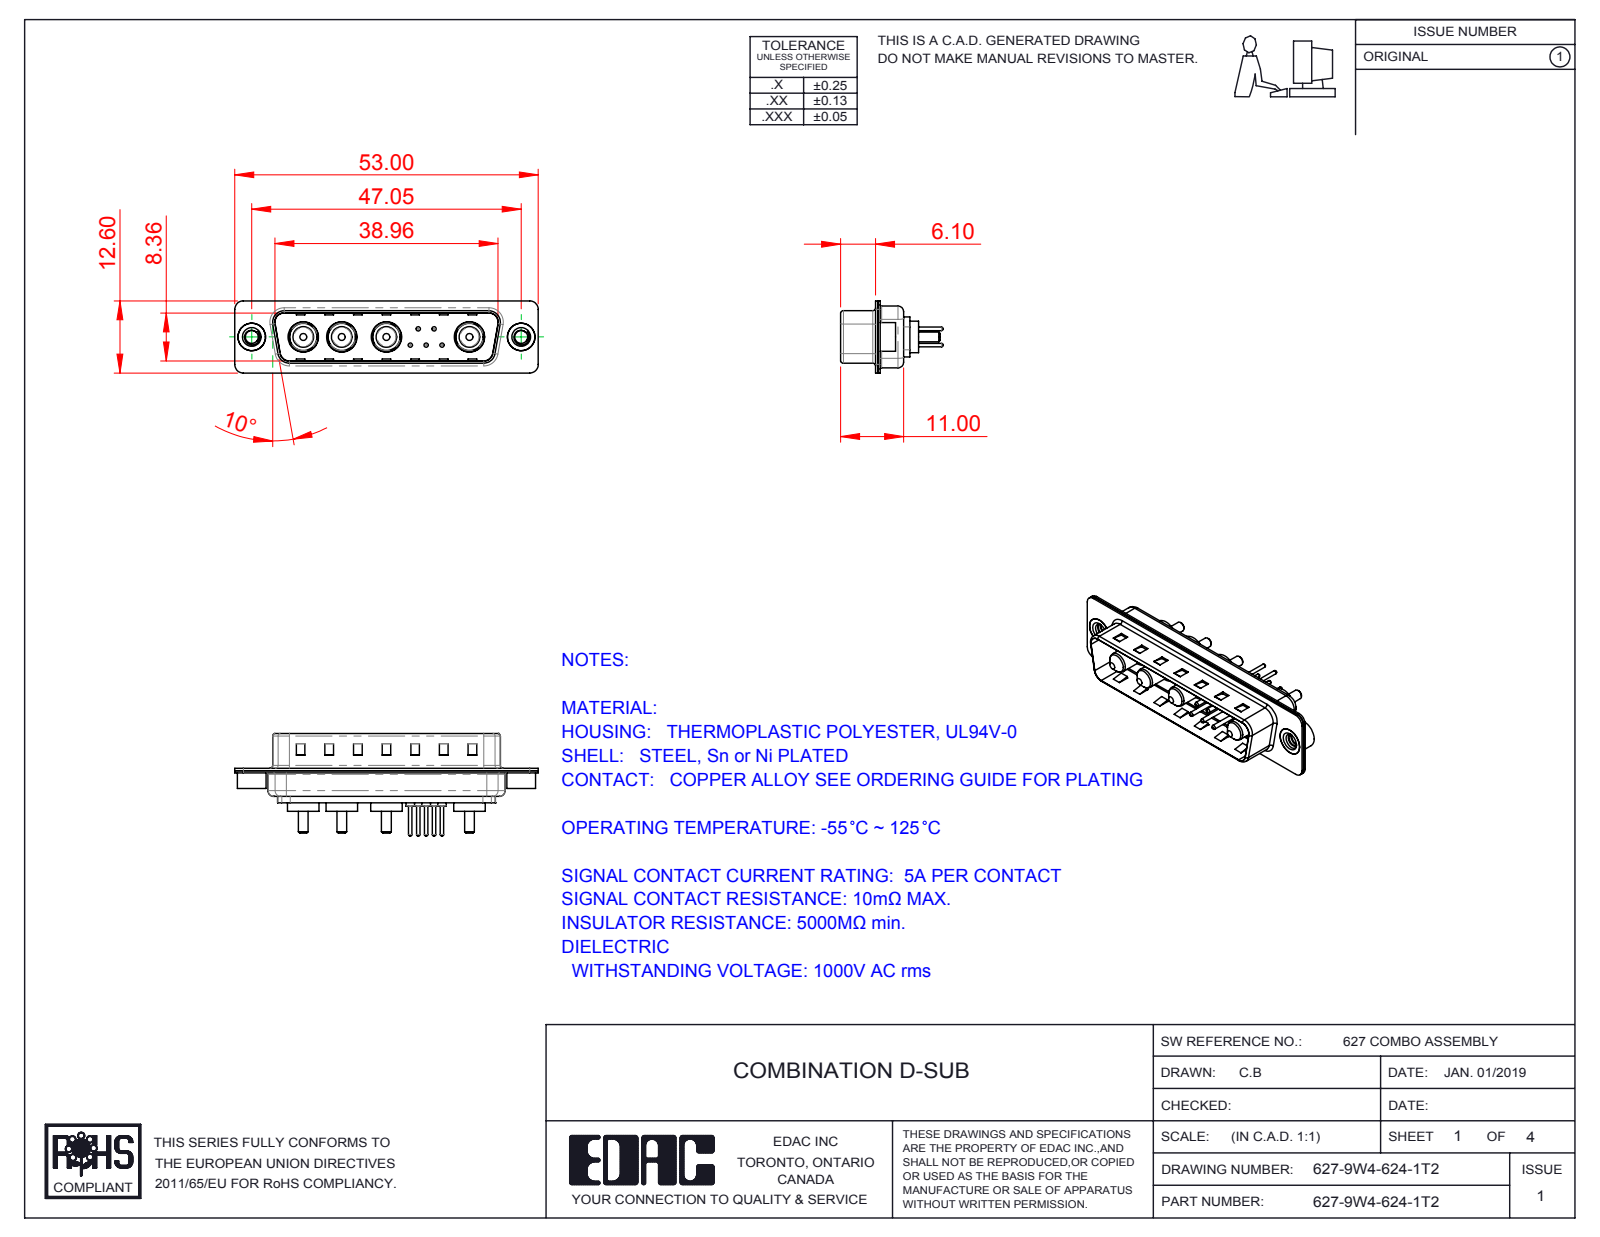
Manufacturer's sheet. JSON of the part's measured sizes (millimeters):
{"part_name": "627Combo Shell Rear_25 Contacts; 627Combo Housing_9W4; 627Combo Contact Row 1_24; 627Combo Contact Row 2_24 (+4 more)", "step_written_by": "SolidWorks 2016 (CONFIG_CONTROL_DESIGN)", "units": "millimeters", "bodies": {"solids": 18, "faces": 721, "planar": 246, "cylindrical": 283, "other": 192}, "overall_size": [53, 17.9, 12.6], "volume_mm3": 2935, "surface_area_mm2": 6659, "round_holes": [[0.75, 5], [1.6, 5], [2, 5], [4.85, 4], [5.3, 4], [2.26, 2], [4, 2], [4.8, 2]], "round_bosses_or_shafts": [[1.5, 5], [0.6, 5], [5.5, 4], [5.2, 4], [4.75, 4], [3.75, 4], [3.6, 4], [1.7, 4]], "partial_cylinders_radius": [[1.5, 16], [2, 12], [0.5, 8], [1.6, 8], [0.25, 4], [0.6, 4], [0.65, 4], [0.9, 4]], "face_to_face_distances": [0.4, 0.82, 9.58, 8.76, 1.5, 0.8, 5.6, 5.2, 1.22, 9.98], "hole_center_spacings": [3.16, 2.77, 5.04, 14.51, 2.78, 4.4, 4.41, 5]}
